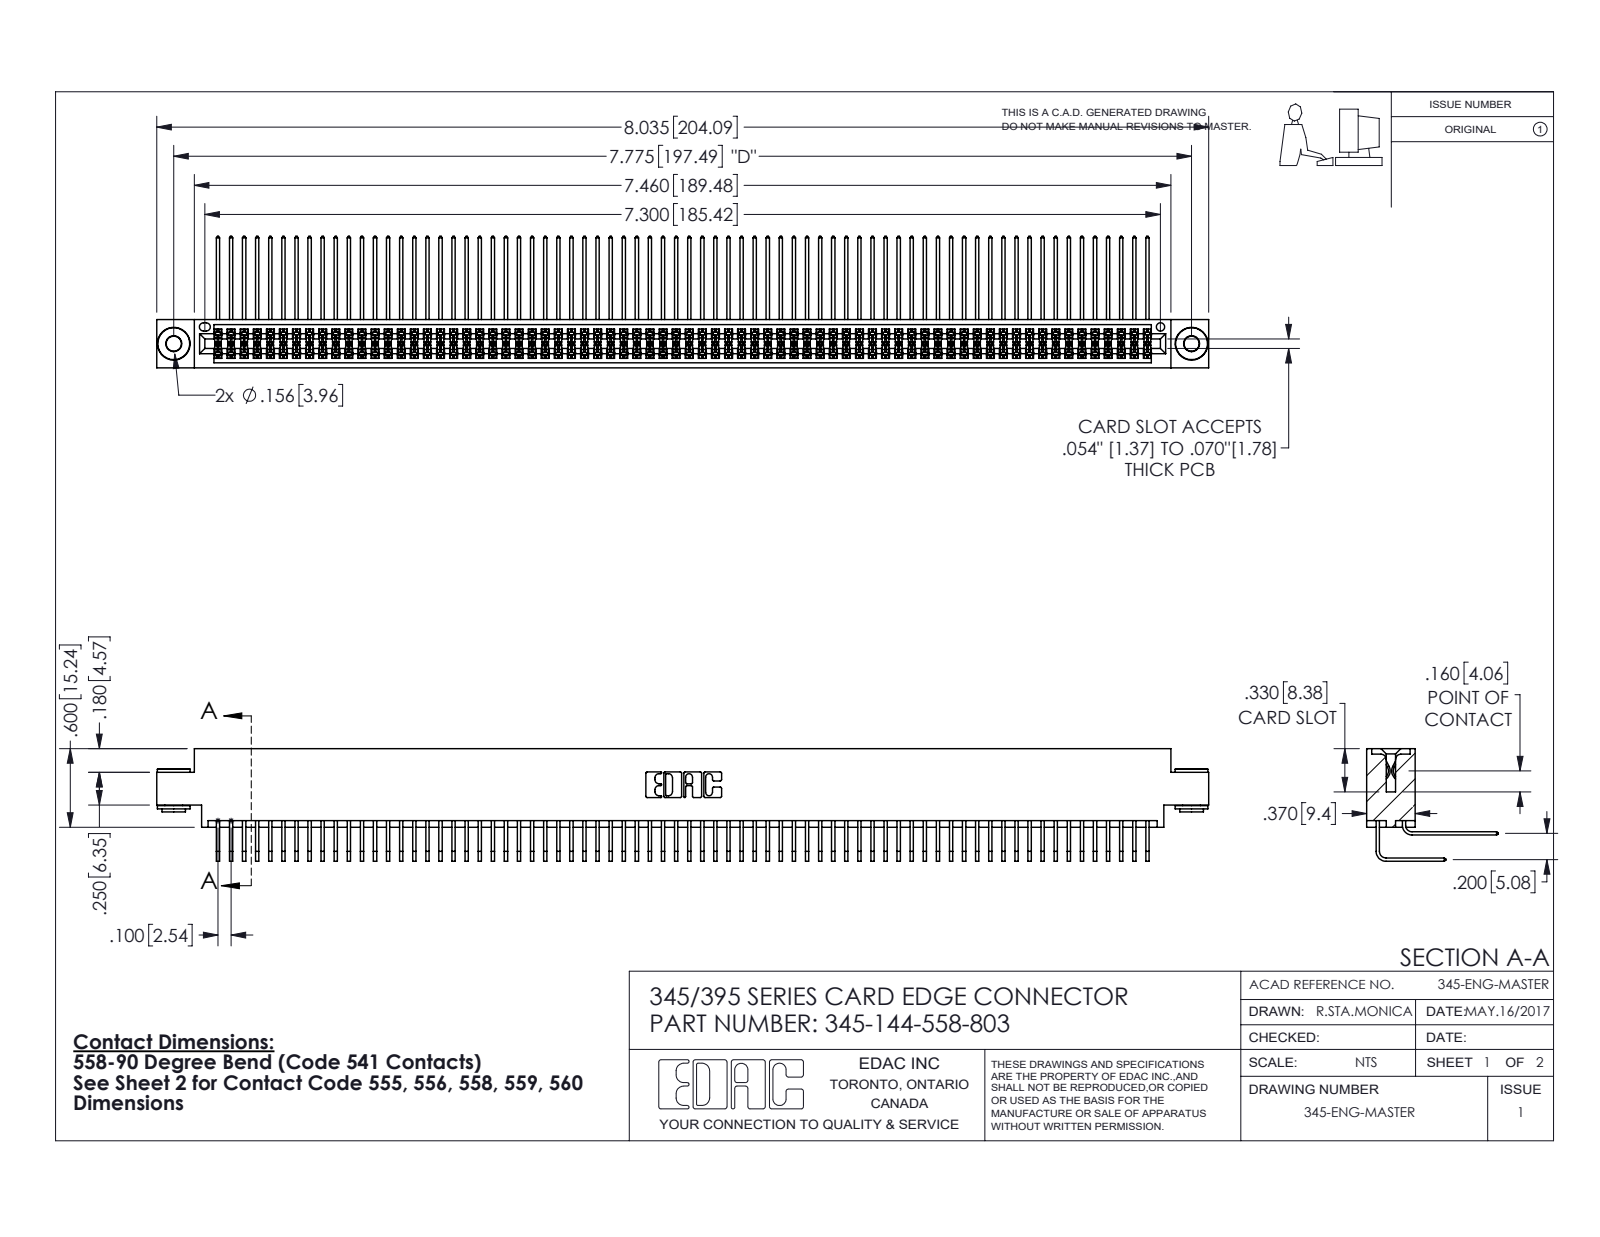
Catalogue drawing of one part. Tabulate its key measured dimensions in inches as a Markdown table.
| quantity | value |
| --- | --- |
| part name | 345-292-001_558 559 Tail - 1; 345-292-001_558 Tail - 2; 345 Part_0.170 Offset - 0.156 Dia-TH; 345-144-558-803 (+1 more) |
| STEP written by | SolidWorks 2016 (CONFIG_CONTROL_DESIGN) |
| units | inches |
| bodies | 147 solids, 7656 faces (5134 planar, 2514 cylindrical, 8 other) |
| overall size | 8.035 × 1.005 × 0.859 |
| volume | 1.272 in³ |
| surface area | 55.24 in² |
| round holes (diameter × count) | 0.116 × 2, 0.156 × 2, 0.064 × 1 |
| round bosses / shafts (diameter × count) | 0.25 × 2, 0.18 × 2, 0.136 × 2 |
| partial cylindrical surfaces (radius × count) | 0.006 × 216, 0.01 × 22, 0.007 × 6, 0.031 × 6, 0.026 × 3, 0.014 × 2, 0.019 × 2, 0.022 × 2 |
| main face-to-face distances | 0.072, 0.298, 0.2, 0.37, 0.098, 0.272, 0.025, 0.225, 0.175, 0.025 |
| hole center spacings | 0.27, 7.539, 7.775 |
